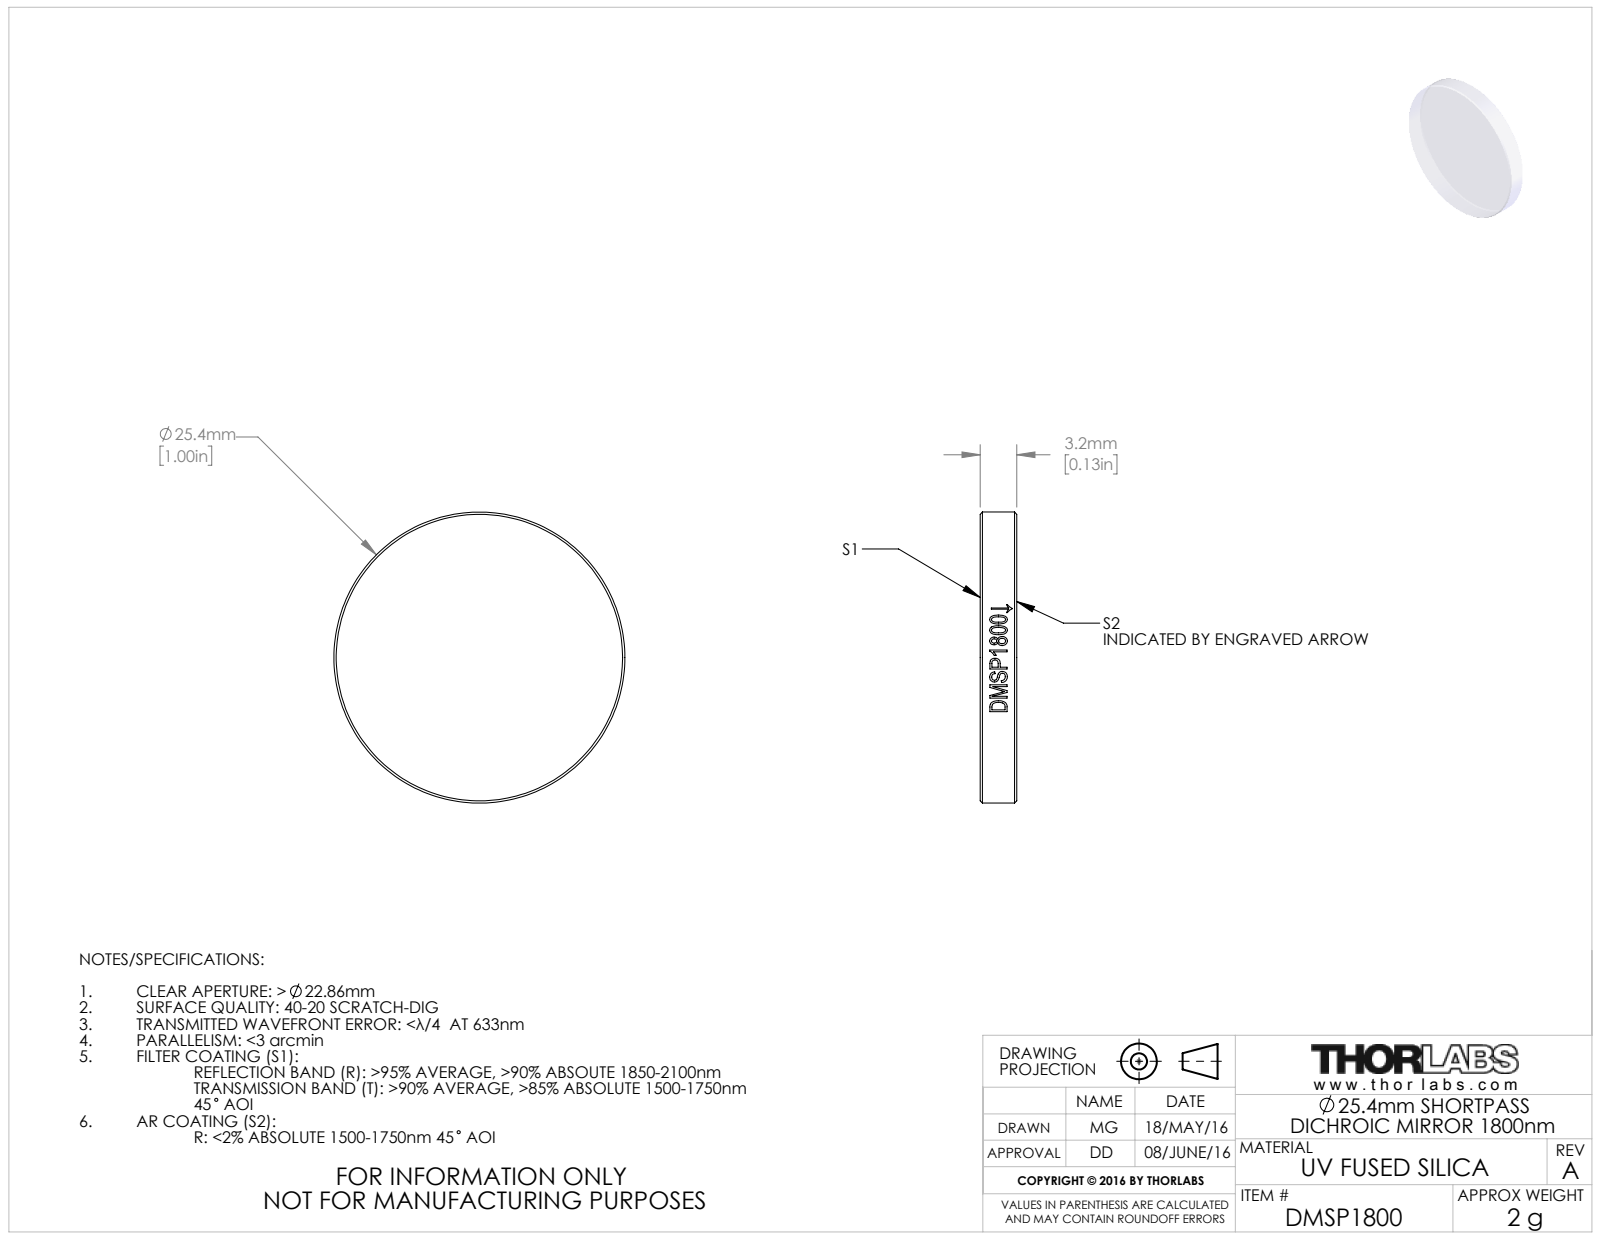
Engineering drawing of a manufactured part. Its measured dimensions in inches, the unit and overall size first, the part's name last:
Units: inches
Overall size (bounding box): 1 × 1 × 0.126
Round bosses / shafts (diameter × count): ⌀1 ×1
Main face-to-face distances: 0.126
Volume: 0.099 in³ · Surface area: 1.938 in²
Bodies: 1 solid, 23 faces (2 planar, 17 cylindrical, 4 other)
Part name (STEP PRODUCT): TTN045161-E0W
STEP written by: SolidWorks 2016 (CONFIG_CONTROL_DESIGN)
